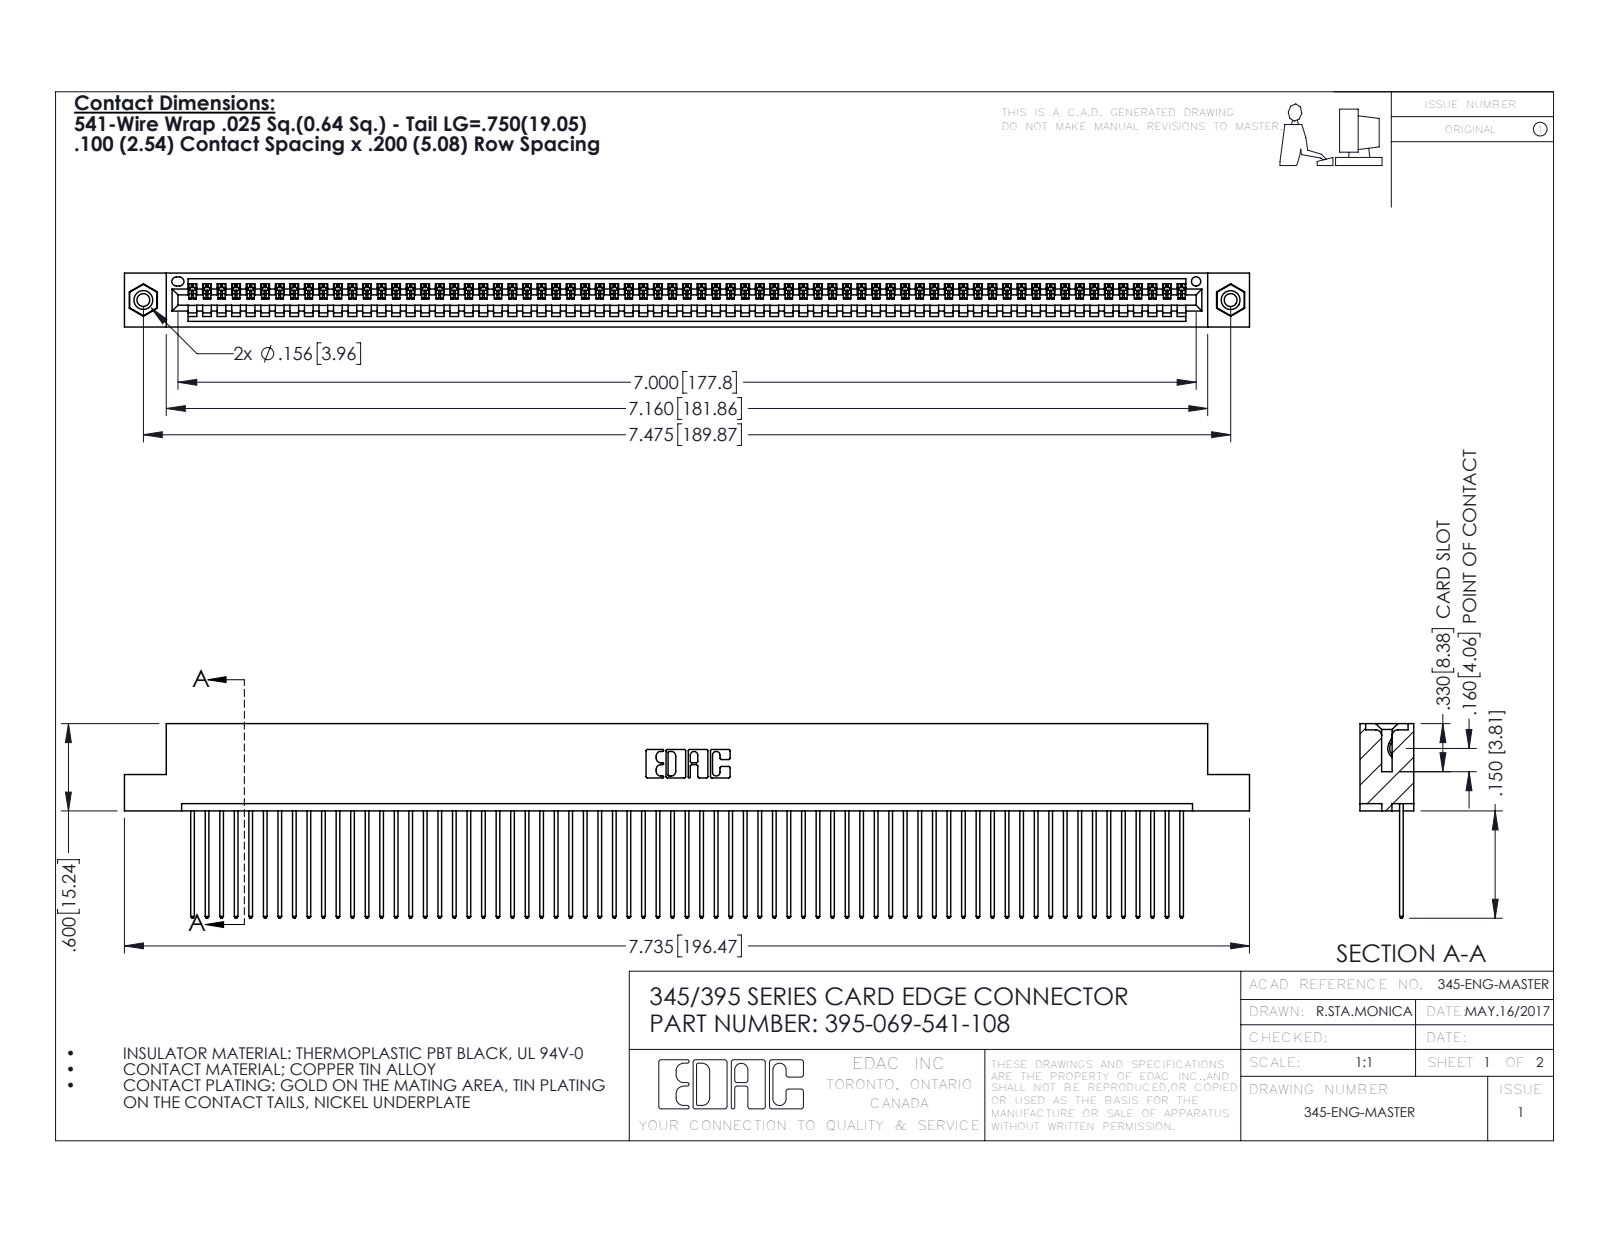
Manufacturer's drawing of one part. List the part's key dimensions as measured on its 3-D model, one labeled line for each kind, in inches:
Part name (STEP PRODUCT): 395-069-541-108; 345 Part_Flush Mounting Lugs - 0.156 Dia-TI; 345-292-001_345-293-141; 345-250-001_345-250-003-102
STEP written by: SolidWorks 2016 (CONFIG_CONTROL_DESIGN)
Units: inches
Bodies: 72 solids, 4188 faces (2872 planar, 1300 cylindrical, 16 other)
Overall size (bounding box): 7.735 × 1.337 × 0.37
Volume: 1.166 in³ · Surface area: 42.02 in²
Round holes (diameter × count): ⌀0.089 ×2, ⌀0.125 ×2, ⌀0.156 ×2, ⌀0.064 ×1
Round bosses / shafts (diameter × count): ⌀0.155 ×2
Partial cylindrical surfaces — rounded edges, fillets, slot ends (radius × count): R0.006 ×138, R0.01 ×138, R0.01 ×22, R0.007 ×6, R0.031 ×6, R0.026 ×3, R0.031 ×2, R0.04 ×2
Main face-to-face distances: 0.072, 0.298, 0.098, 0.272, 0.025, 0.37, 0.2, 0.225, 0.149, 0.072
Hole centre spacings: 0.27, 7.239, 7.475
